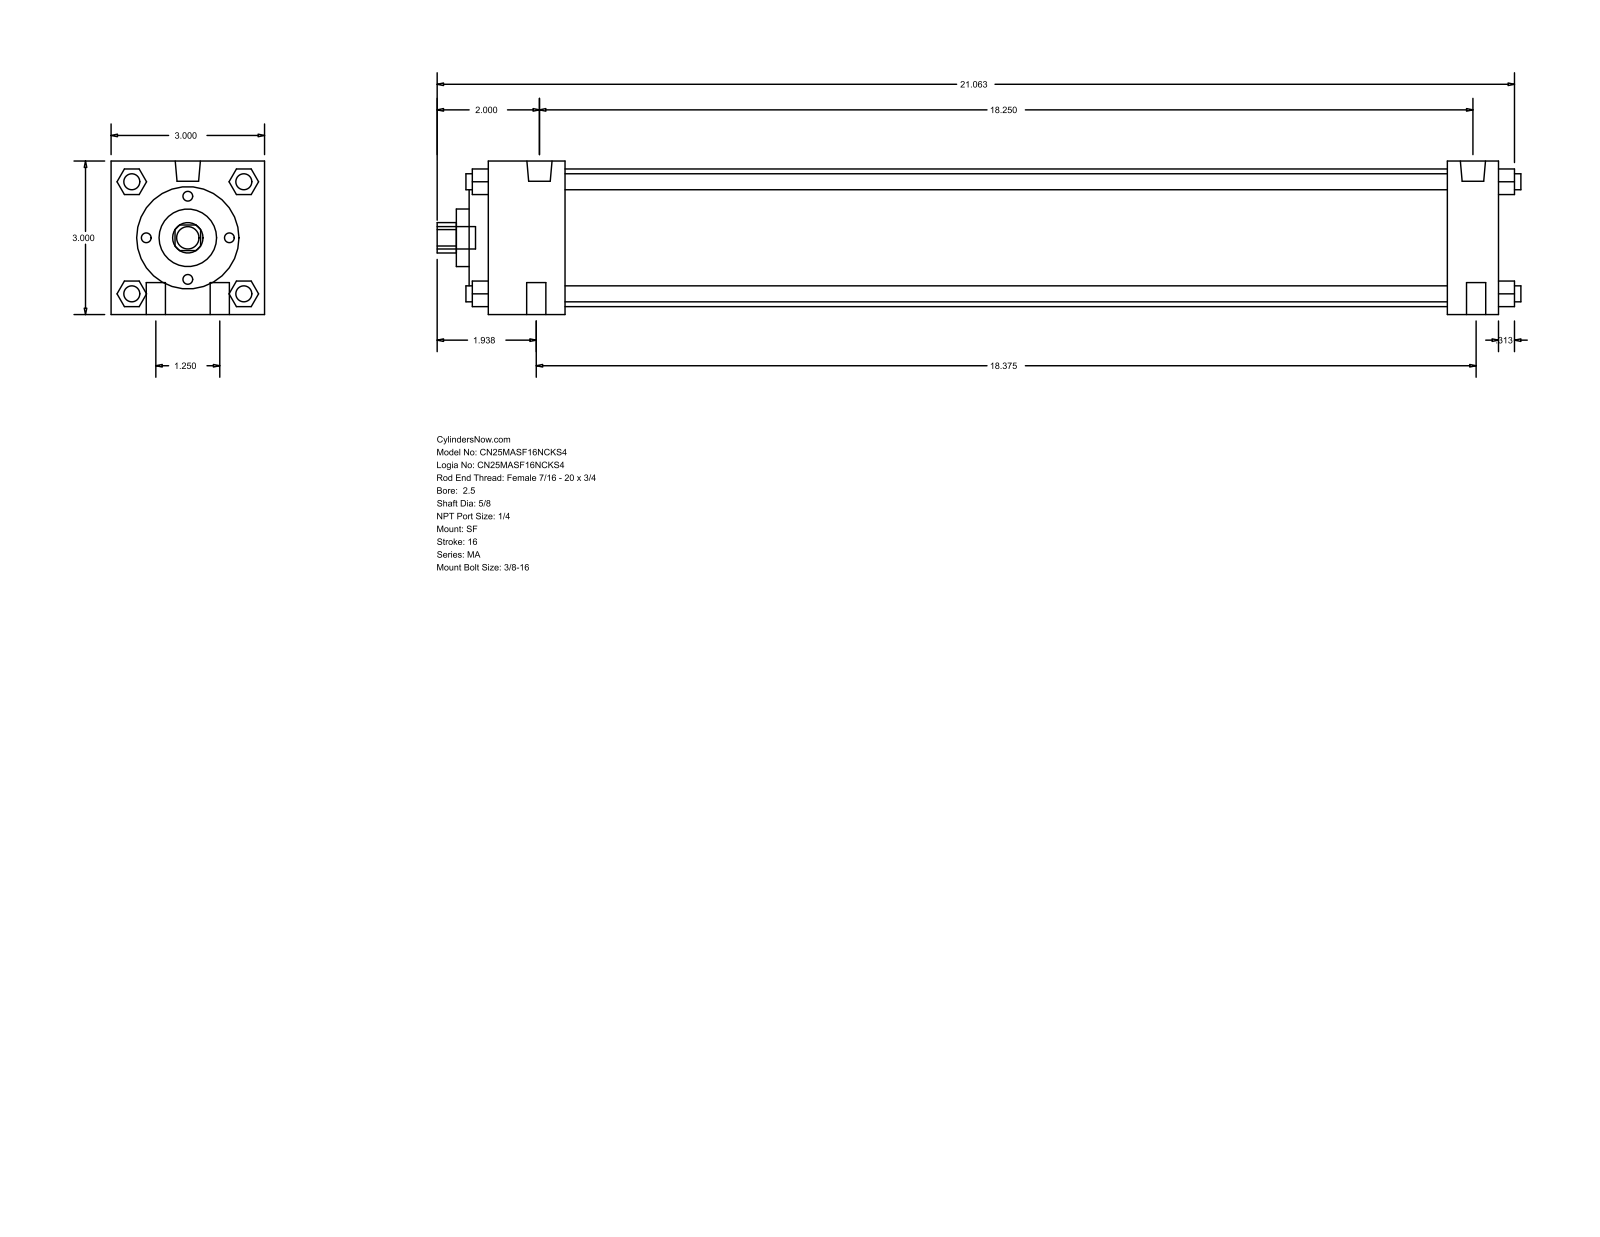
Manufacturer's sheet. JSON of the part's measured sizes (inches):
{"part_name": "MA_SF__0250_0.625", "step_written_by": "GSSL Pune (CONFIG_CONTROL_DESIGN)", "units": "inches", "bodies": {"solids": 0, "faces": 126, "planar": 95, "cylindrical": 31, "other": 0}, "overall_size": [21.187, 3, 3], "round_holes": [[0.625, 1], [1.125, 1], [2, 1], [2.69, 1]], "round_bosses_or_shafts": [[0.313, 6], [0.375, 4], [0.492, 2], [0.437, 1]], "partial_cylinders_radius": [[0.297, 1]], "face_to_face_distances": [3, 19.75, 1, 18.75, 1.5, 17.25, 18.25, 0.5, 0.375, 1.875]}
